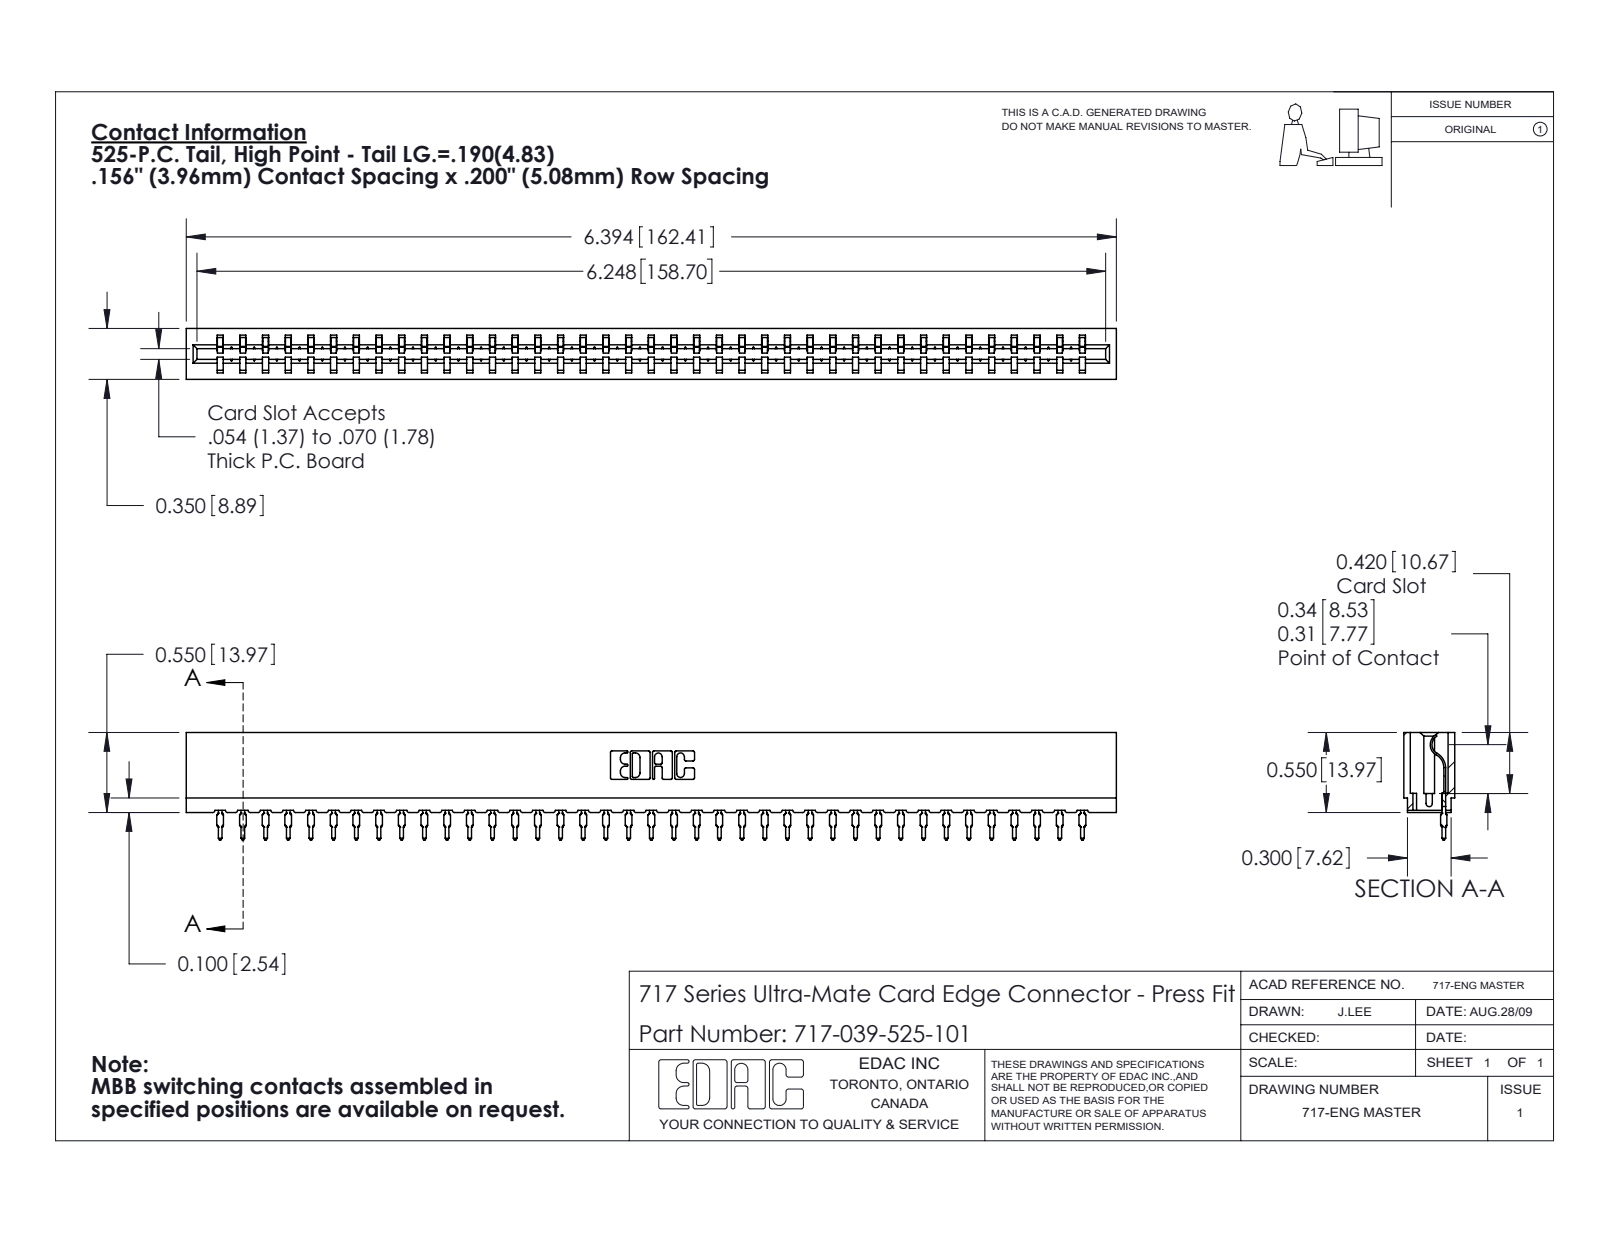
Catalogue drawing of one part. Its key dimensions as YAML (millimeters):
part_name: "717-039-525-101; 717 Part_Insulator Option - 06; 745-292-001_525"
step_written_by: "SolidWorks 2020 (CONFIG_CONTROL_DESIGN)"
units: millimeters
bodies: {solids: 40, faces: 4501, planar: 2706, cylindrical: 781, other: 1014}
overall_size: [162.4, 18.8, 8.9]
volume: 13700
surface_area: 19080
partial_cylinders:
  - {radius: 0.4, count: 78}
  - {radius: 0.5, count: 78}
  - {radius: 0.3, count: 22}
  - {radius: 0.2, count: 6}
  - {radius: 0.8, count: 6}
  - {radius: 0.1, count: 4}
  - {radius: 0.3, count: 4}
  - {radius: 0.7, count: 3}
face_to_face_distances: [5.4, 3.5, 8.9, 1.9, 1.1, 7.7, 2.4, 4.2, 0.6, 1.6]
